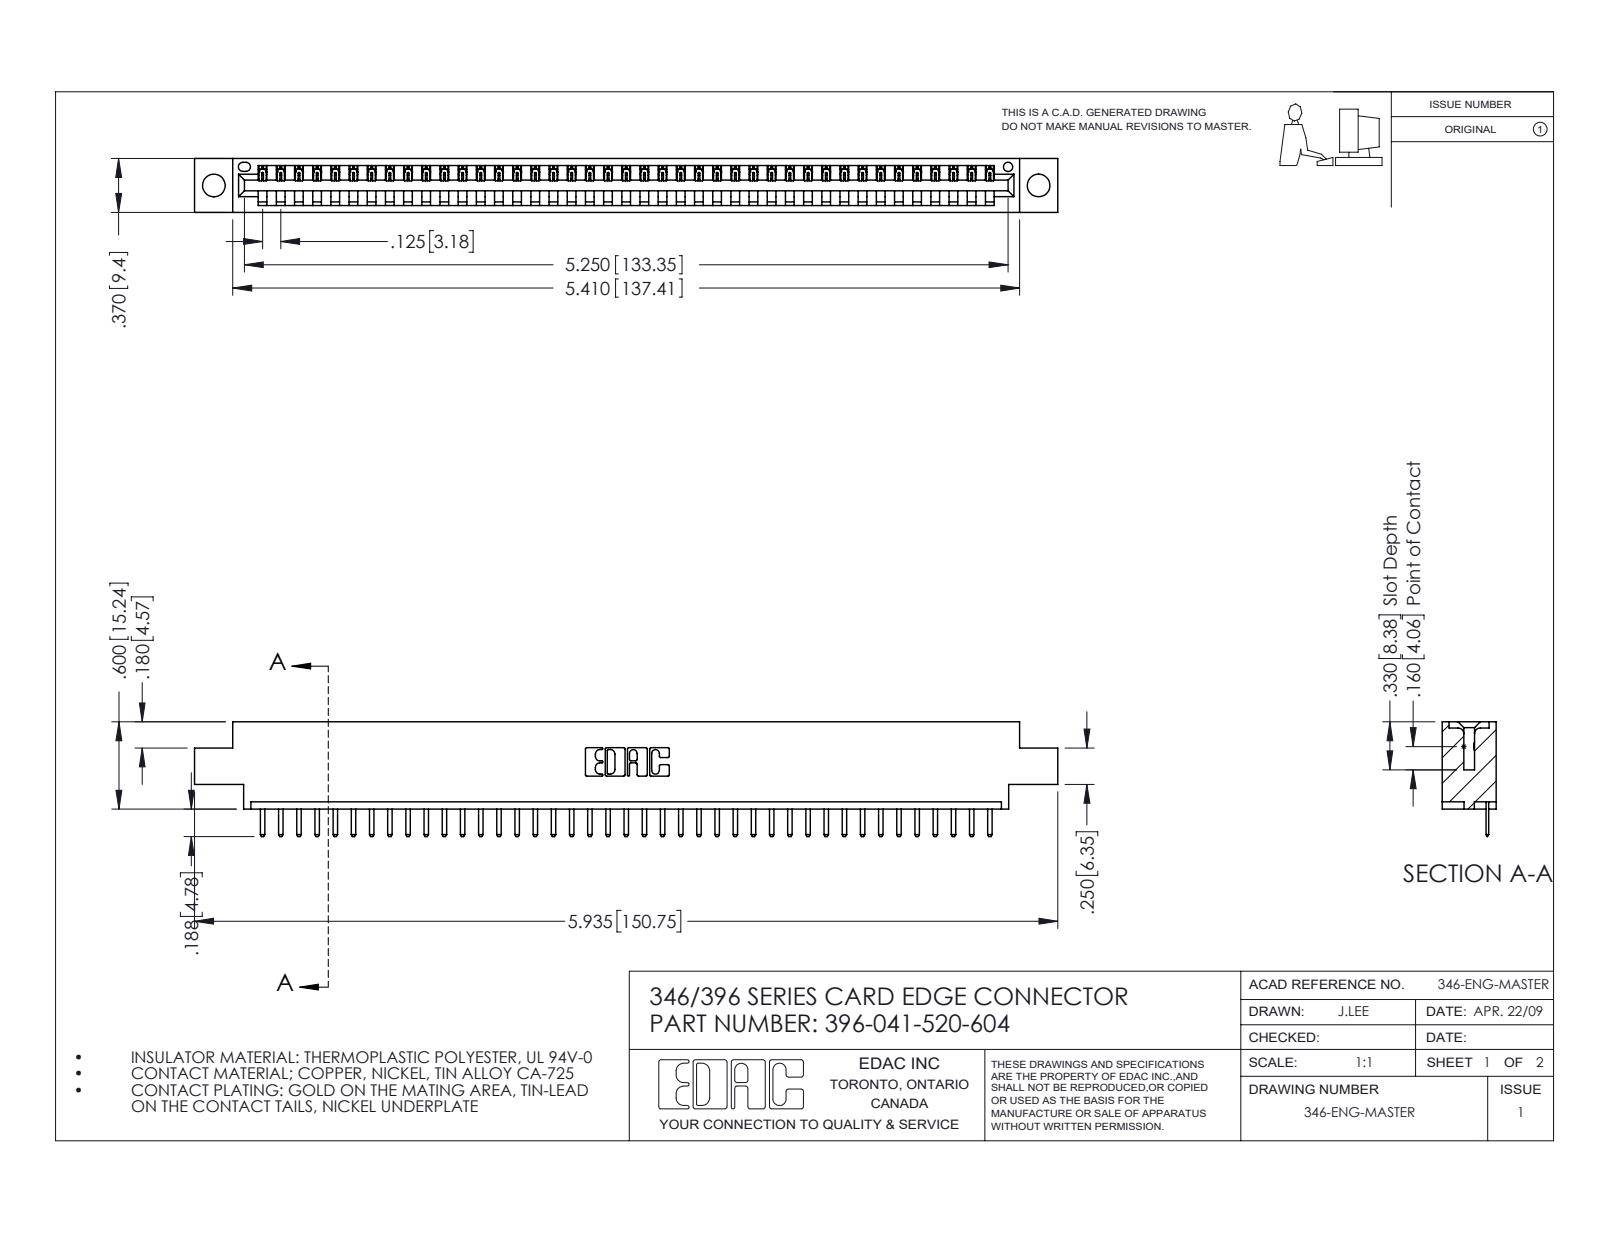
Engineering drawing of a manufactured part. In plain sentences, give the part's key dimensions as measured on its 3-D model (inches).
The part is named "346 Part_0.170 Offset - 0.156 Dia-TH; 396-041-520-604; 345-292-001_345-293-120". Its 3-D file was written by "SolidWorks 2016 (CONFIG_CONTROL_DESIGN)". It is 42 solids with 2668 faces: 1802 planar, 866 cylindrical and 0 other. Overall it measures 5.935 by 0.788 by 0.37 inches. Its volume is 0.858 cubic inches and its surface area 26.56 square inches. Round holes: 2 of diameter 0.156, 1 of diameter 0.064. Partial cylindrical surfaces (rounded edges, fillets, slot ends): 84 of radius 0.01, 82 of radius 0.006, 22 of radius 0.01, 6 of radius 0.007, 6 of radius 0.031, 3 of radius 0.026, 2 of radius 0.031, 2 of radius 0.04. The main face-to-face distances are 0.048, 0.322, 0.37, 0.25, 0.148, 0.222, 0.1, 0.174, 0.072, 0.298. The hole center spacings are 0.246, 5.461, 5.67.
